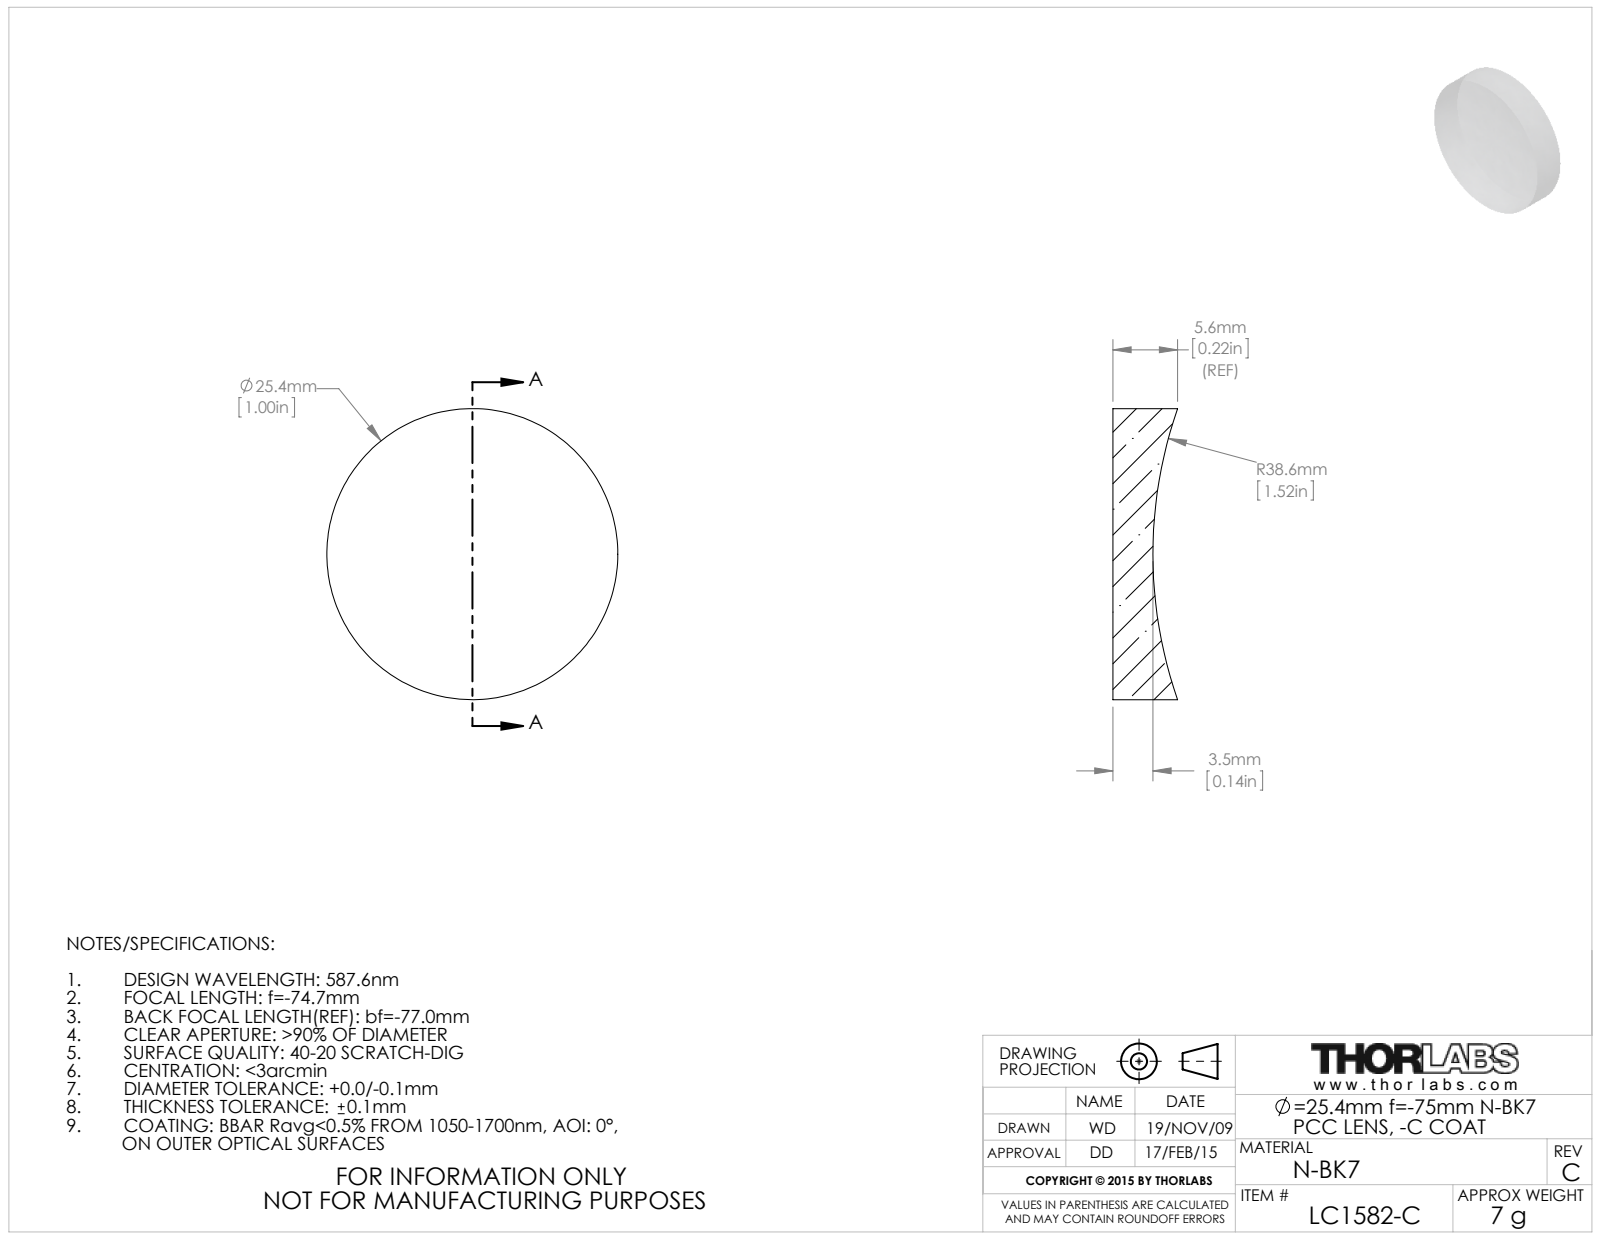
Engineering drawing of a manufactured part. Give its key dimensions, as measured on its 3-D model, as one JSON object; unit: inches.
{"part_name": "4805-E0W", "step_written_by": "SolidWorks 2009 (AUTOMOTIVE_DESIGN)", "units": "inches", "bodies": {"solids": 1, "faces": 5, "planar": 1, "cylindrical": 2, "other": 2}, "overall_size": [1, 1, 0.222], "volume_in3": 0.141, "surface_area_in2": 2.292, "round_bosses_or_shafts": [[1, 1]]}
